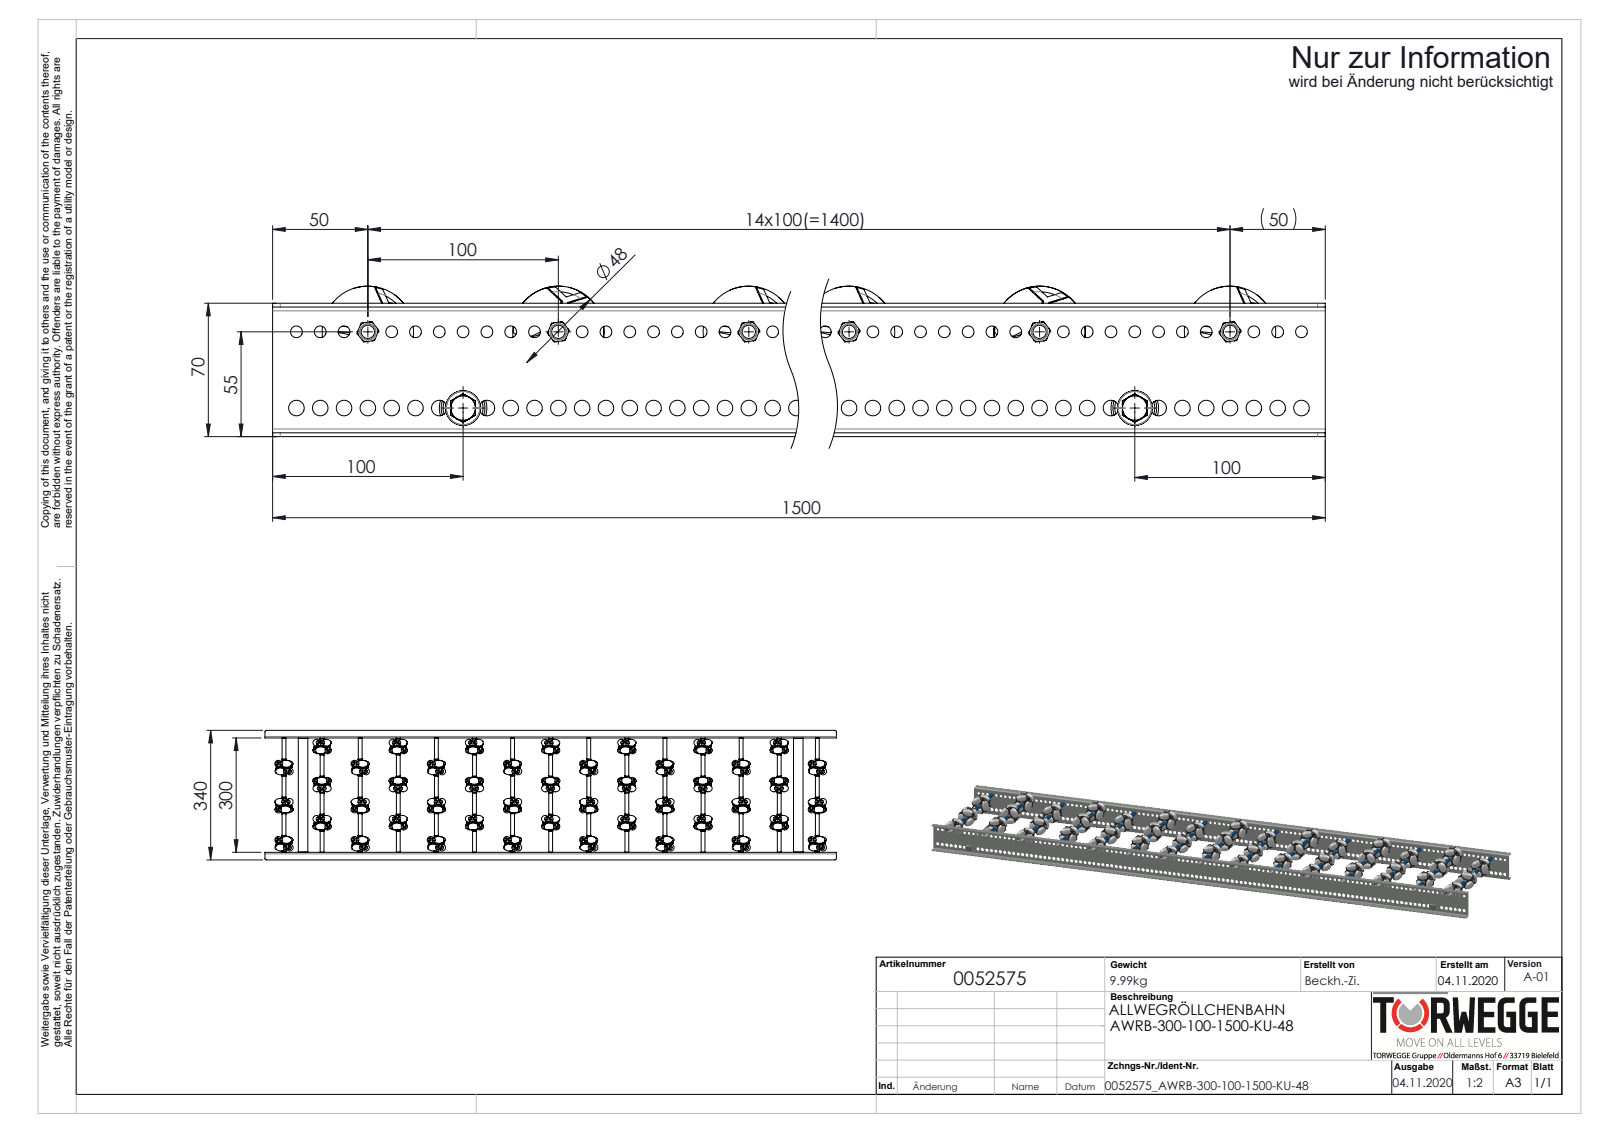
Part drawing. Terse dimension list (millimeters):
name: AWR48_Halter; 0019719_Gewindestange-M6_L=320; 0015028_AWR48; 0019730_Tragrollenrohr-Ø10x1,75KU_KFG_0019730_L=55 (+8 more)
written by: SolidWorks 2020 (AUTOMOTIVE_DESIGN)
unit: mm
bodies: 777 solids, 14462 faces (4800 planar, 5838 cylindrical, 3824 other)
size: 1500 × 340 × 79
volume: 2 869 000 mm³; area: 2 085 000 mm²
holes: 270× ⌀3.7, 270× ⌀4.2, 119× ⌀6.2, 119× ⌀8.2, 15× ⌀4.92, 15× ⌀6.5, 15× ⌀8.4, 2× ⌀6.8, 2× ⌀21
bosses: 270× ⌀4, 246× ⌀3.7, 17× ⌀8, 15× ⌀42, 15× ⌀11, 15× ⌀10, 15× ⌀7, 15× ⌀6
rounds: 15× R23.55, 8× R4, 4× R2
face distances: 2, 302, 68, 300, 304, 70, 66, 20, 3, 5
hole spacings: 36.06, 36.05, 8, 169.07, 81.84, 90.03, 354.1, 88.42
